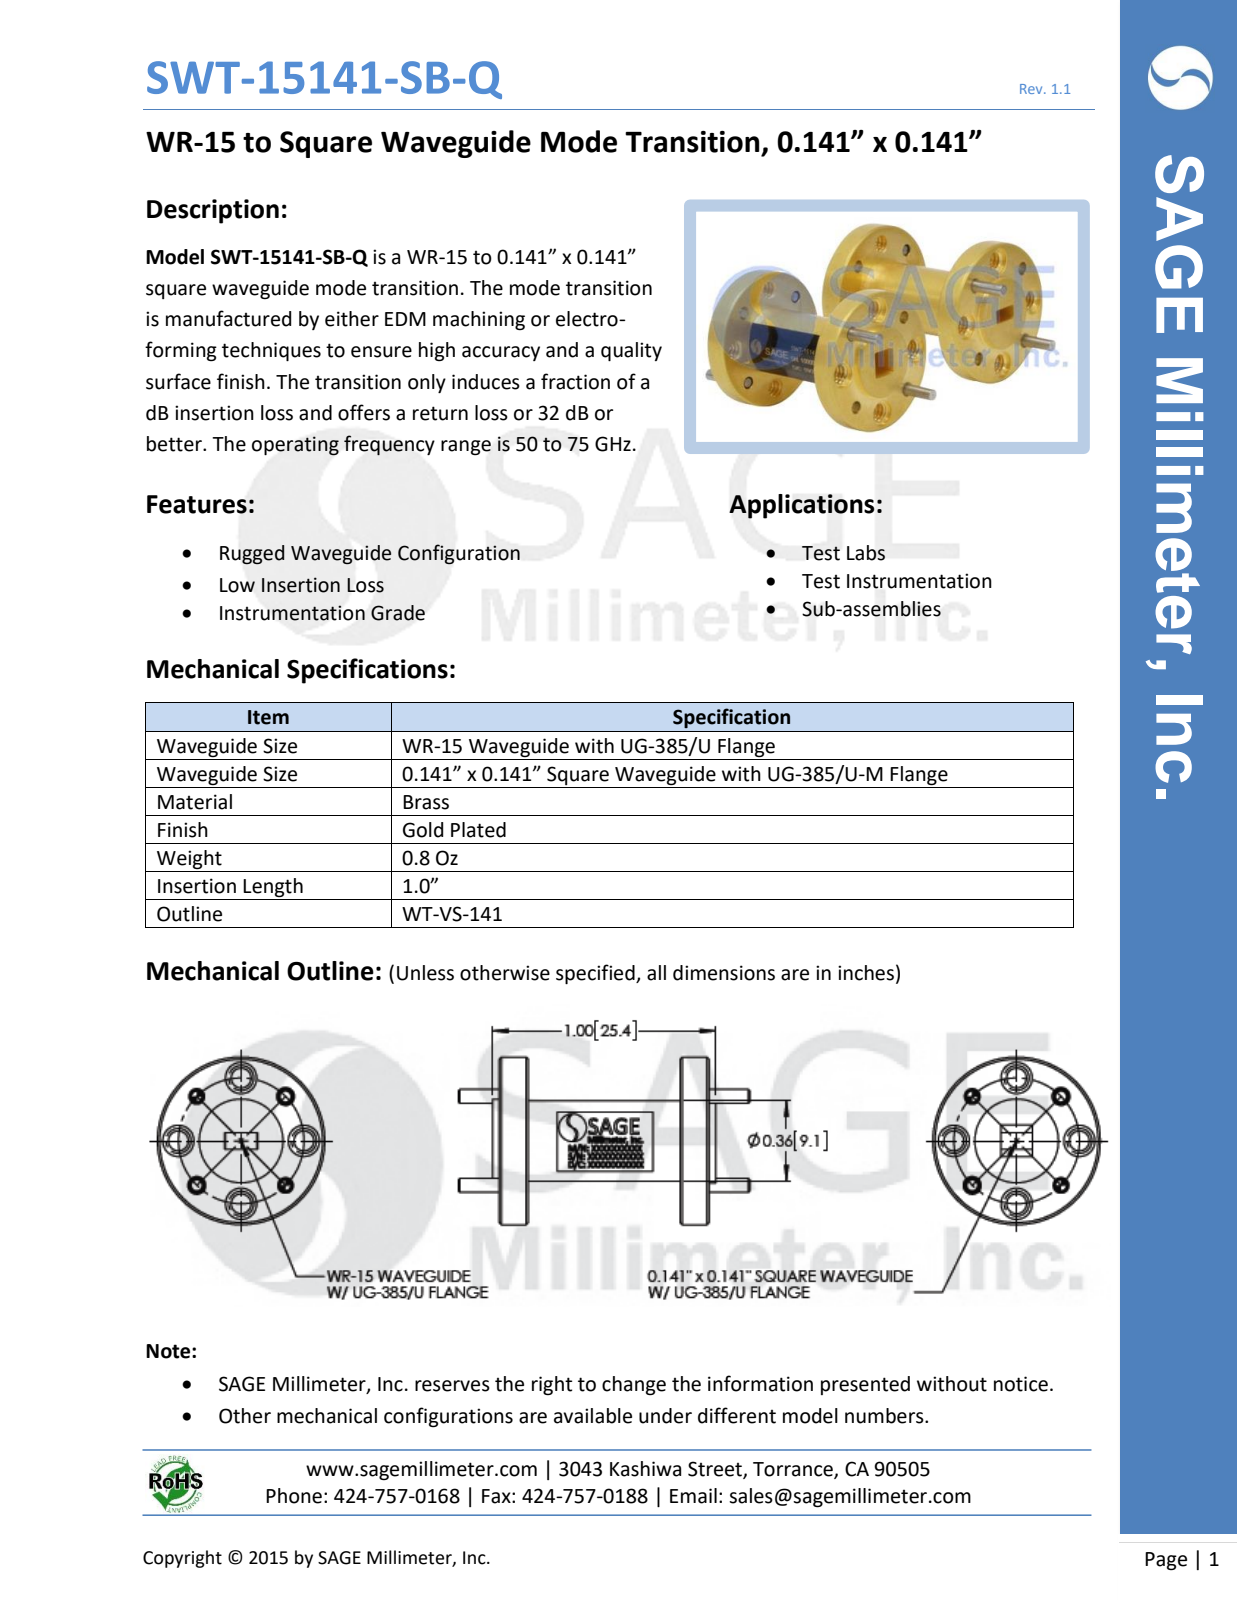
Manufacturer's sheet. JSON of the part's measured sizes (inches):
{"part_name": "SWT-15141-SB-Q, CTRLD", "step_written_by": "SolidWorks 2013 (CONFIG_CONTROL_DESIGN)", "units": "inches", "bodies": {"solids": 5, "faces": 132, "planar": 26, "cylindrical": 66, "other": 40}, "overall_size": [1.305, 0.75, 0.75], "volume_in3": 0.167, "surface_area_in2": 4.065, "round_holes": [[0.06, 4], [0.067, 4], [0.089, 4], [0.14, 4]], "round_bosses_or_shafts": [[0.063, 4], [0.75, 1], [0.375, 1], [0.36, 1]], "face_to_face_distances": [0.13, 0.81, 0.68, 0.94, 0.97, 0.84, 0.16, 0.03, 0.03, 0.16], "hole_center_spacings": [0.215, 0.398, 0.519, 0.52, 0.562, 0.563, 0.398]}
